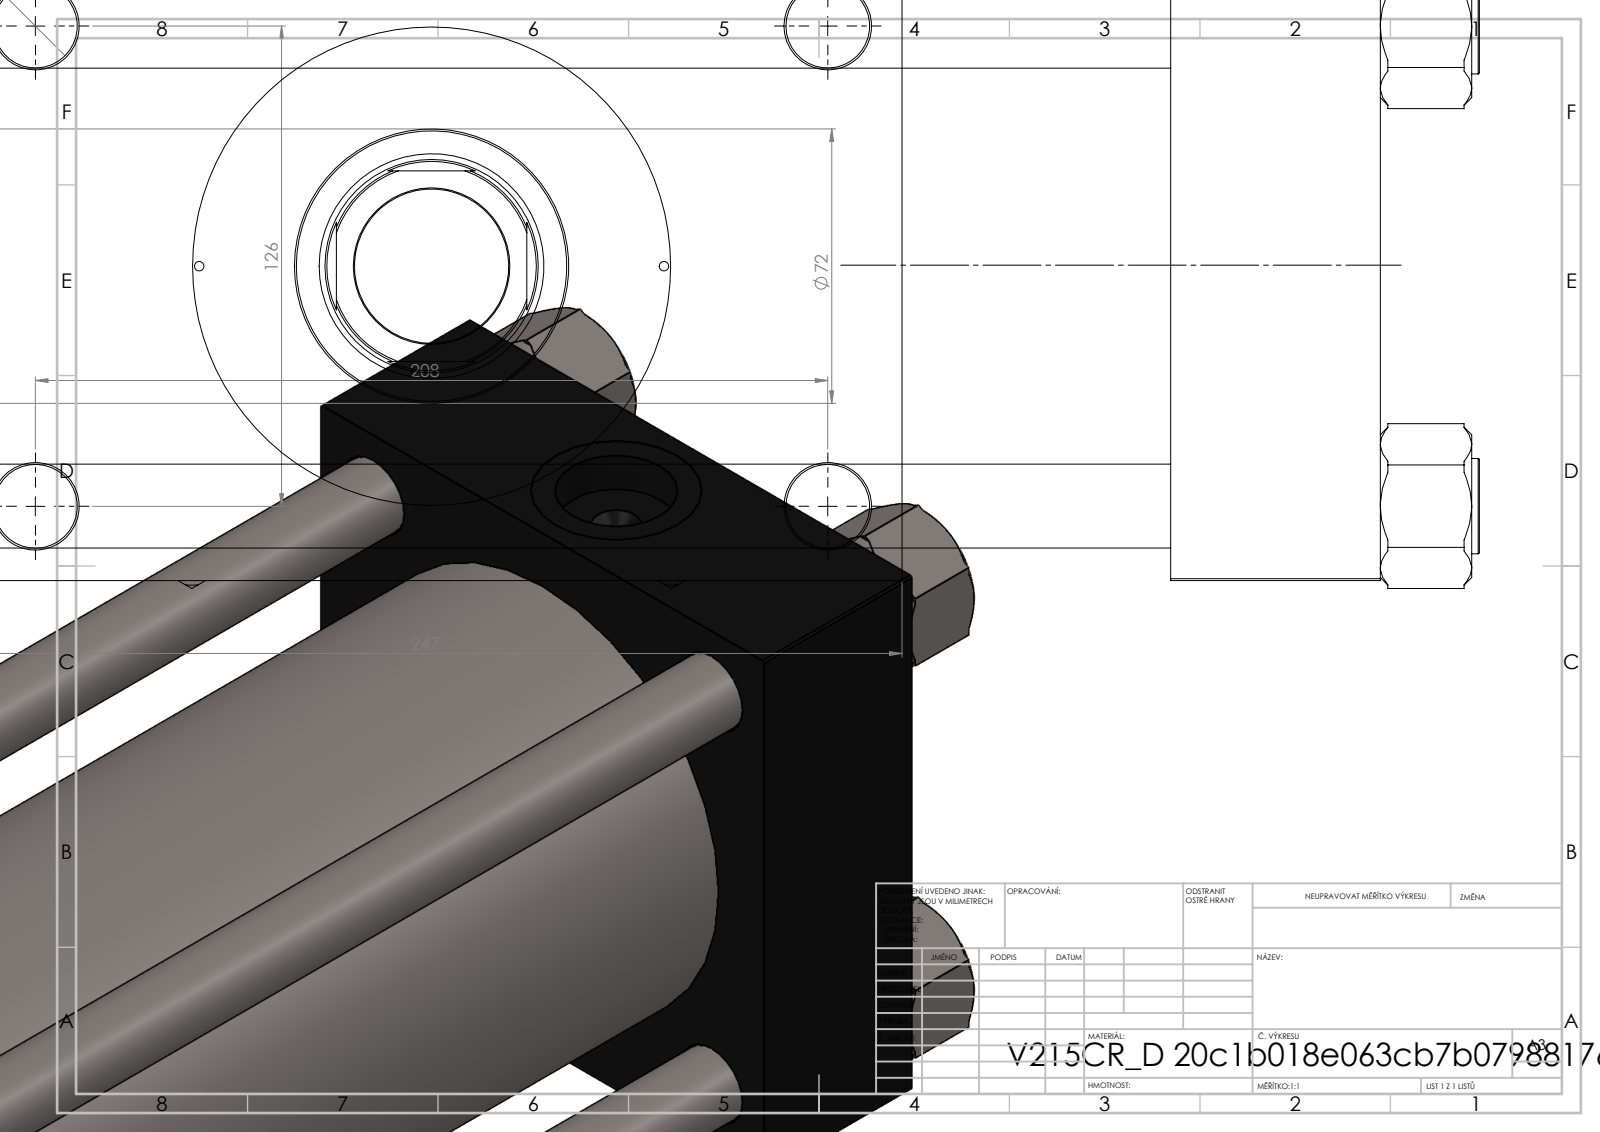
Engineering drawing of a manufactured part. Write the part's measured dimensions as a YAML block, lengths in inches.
part_name: "V215CR_VCP_D; V215CR_D_TYCINKA; NUT_M5_D; V215CR_D_Body (+1 more)"
step_written_by: "SolidWorks 2019 (CONFIG_CONTROL_DESIGN)"
units: inches
bodies: {solids: 11, faces: 1155, planar: 546, cylindrical: 91, other: 518}
overall_size: [20, 9.724, 6.659]
volume: 375.4
surface_area: 1269
round_holes:
  - {diameter: 0.866, count: 8}
  - {diameter: 0.098, count: 2}
  - {diameter: 0.276, count: 2}
  - {diameter: 1.269, count: 2}
  - {diameter: 1.772, count: 2}
  - {diameter: 1.594, count: 1}
  - {diameter: 2.205, count: 1}
  - {diameter: 2.323, count: 1}
  - {diameter: 3.78, count: 1}
  - {diameter: 4.921, count: 1}
  - {diameter: 4.941, count: 1}
round_bosses_or_shafts:
  - {diameter: 0.984, count: 4}
  - {diameter: 5.157, count: 1}
  - {diameter: 2.835, count: 1}
partial_cylinders:
  - {radius: 1.063, count: 1}
face_to_face_distances: [12.362, 6.496, 2.165, 14.528, 2.205, 16.732, 14.567, 1.614, 8.11, 15.895]
hole_center_spacings: [1.616, 2.48, 3.003, 3.505, 4.787, 4.957, 5.215, 5.473]
